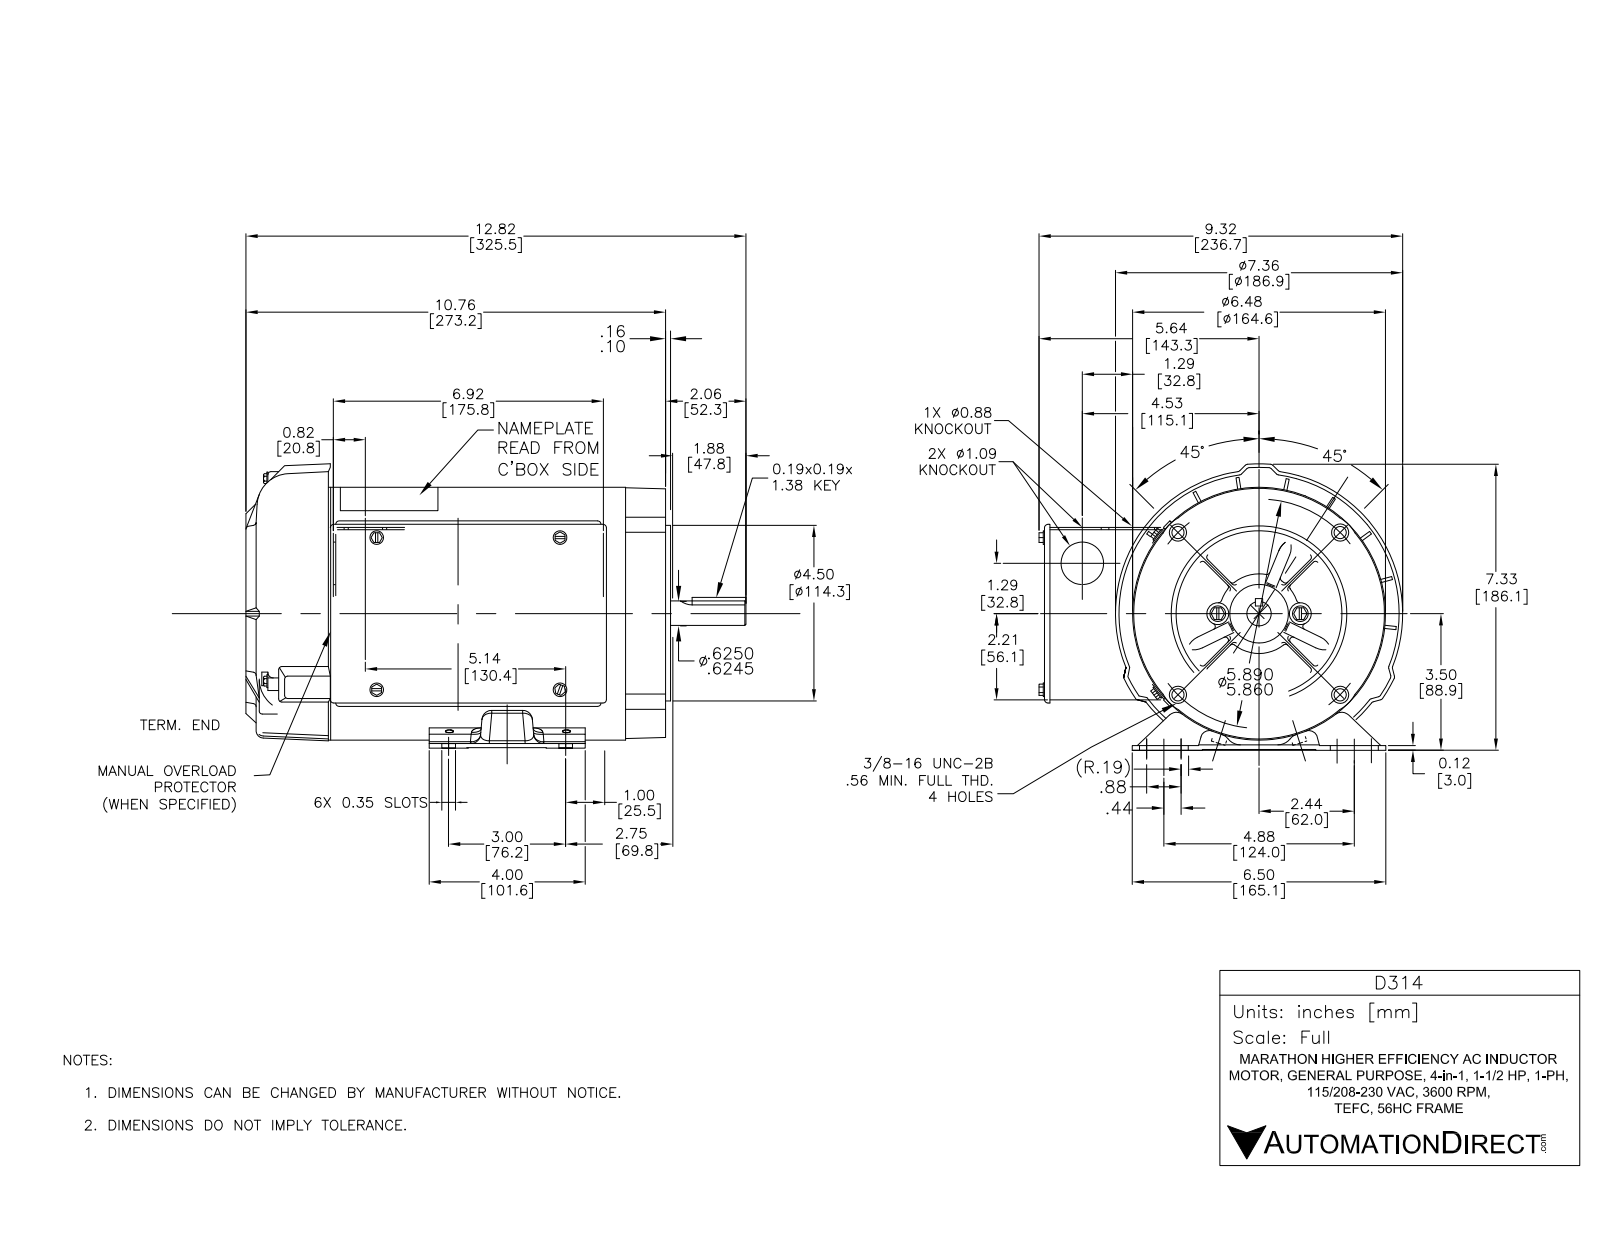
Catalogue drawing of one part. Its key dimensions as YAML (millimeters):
part_name: "SS69971-675_Rev00"
step_written_by: "SolidWorks 2015 (CONFIG_CONTROL_DESIGN)"
units: millimeters
bodies: {solids: 32, faces: 2638, planar: 720, cylindrical: 527, other: 1391}
overall_size: [416.6, 345.7, 284.3]
volume: 3577000
surface_area: 1147000
round_holes:
  - {diameter: 5.1, count: 11}
  - {diameter: 3, count: 10}
  - {diameter: 11.1, count: 8}
  - {diameter: 4, count: 5}
  - {diameter: 8, count: 5}
  - {diameter: 2.2, count: 4}
  - {diameter: 5.9, count: 4}
  - {diameter: 6, count: 4}
  - {diameter: 7.9, count: 4}
  - {diameter: 8.4, count: 4}
  - {diameter: 19.1, count: 3}
  - {diameter: 2.3, count: 2}
round_bosses_or_shafts:
  - {diameter: 6.4, count: 6}
  - {diameter: 12.7, count: 4}
  - {diameter: 5.5, count: 4}
  - {diameter: 8.9, count: 2}
  - {diameter: 7.1, count: 2}
  - {diameter: 5.6, count: 2}
  - {diameter: 4, count: 2}
  - {diameter: 211.5, count: 1}
partial_cylinders:
  - {radius: 3, count: 59}
  - {radius: 6.4, count: 49}
  - {radius: 4.1, count: 18}
  - {radius: 1.5, count: 6}
  - {radius: 7.9, count: 5}
  - {radius: 13.5, count: 4}
  - {radius: 14.2, count: 4}
  - {radius: 22.4, count: 4}
face_to_face_distances: [3.2, 71, 9.4, 74.2, 62.7, 67.8, 72.1, 13.5, 264.2, 3]
hole_center_spacings: [82.6, 60.6, 63.2, 72.2, 111.3, 116.7, 125.5, 130.3]
